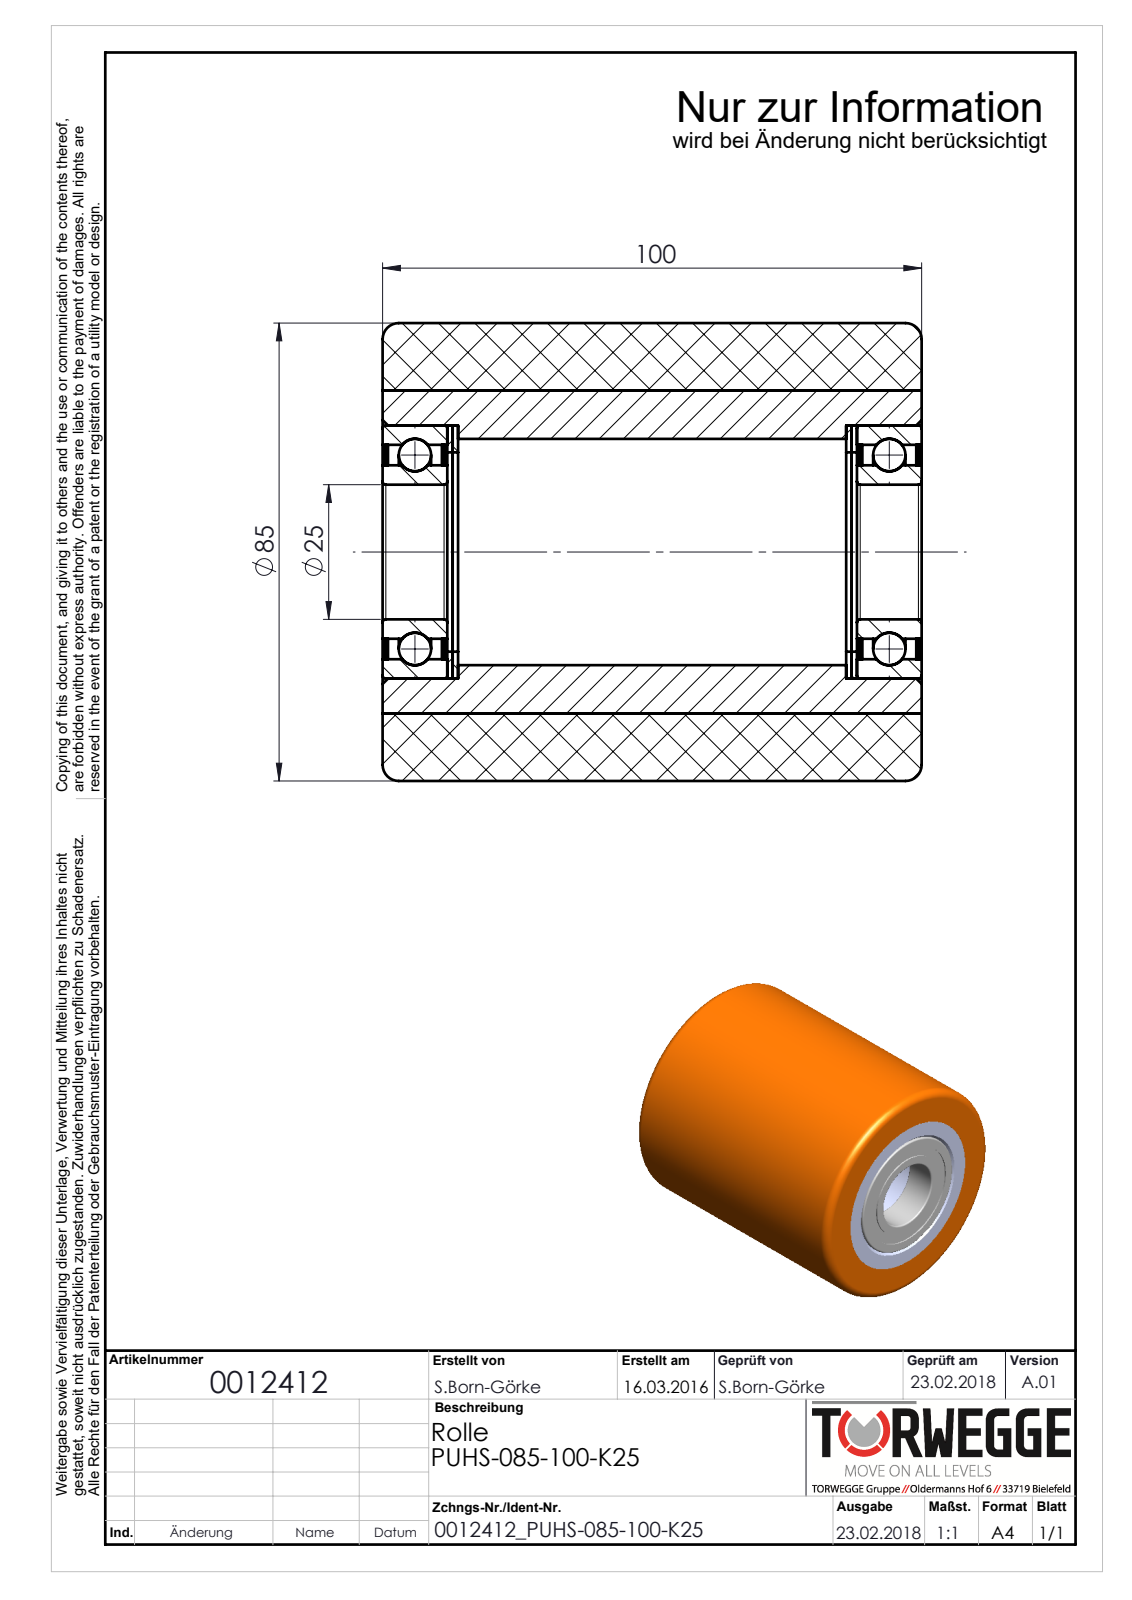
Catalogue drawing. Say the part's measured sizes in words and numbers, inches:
The part is named "0012412_PUHS-085-100-K25". Its 3-D file was written by "SolidWorks 2016 (AUTOMOTIVE_DESIGN)". It is 16 solids with 158 faces: 30 planar, 68 cylindrical and 60 other. Overall it measures 3.937 by 3.346 by 3.346 inches. Its volume is 27.18 cubic inches and its surface area 177.2 square inches. Round holes: 1 of diameter 0.984, 1 of diameter 1.268, 1 of diameter 1.457, 1 of diameter 1.567, 1 of diameter 1.654, 1 of diameter 2.362. Round bosses or shafts: 1 of diameter 3.346, 1 of diameter 1.85. The main face-to-face distances are 0.039, 3.465, 3.937, 0.472, 0.02, 0.512, 3.425, 2.953, 2.913, 3.386.
